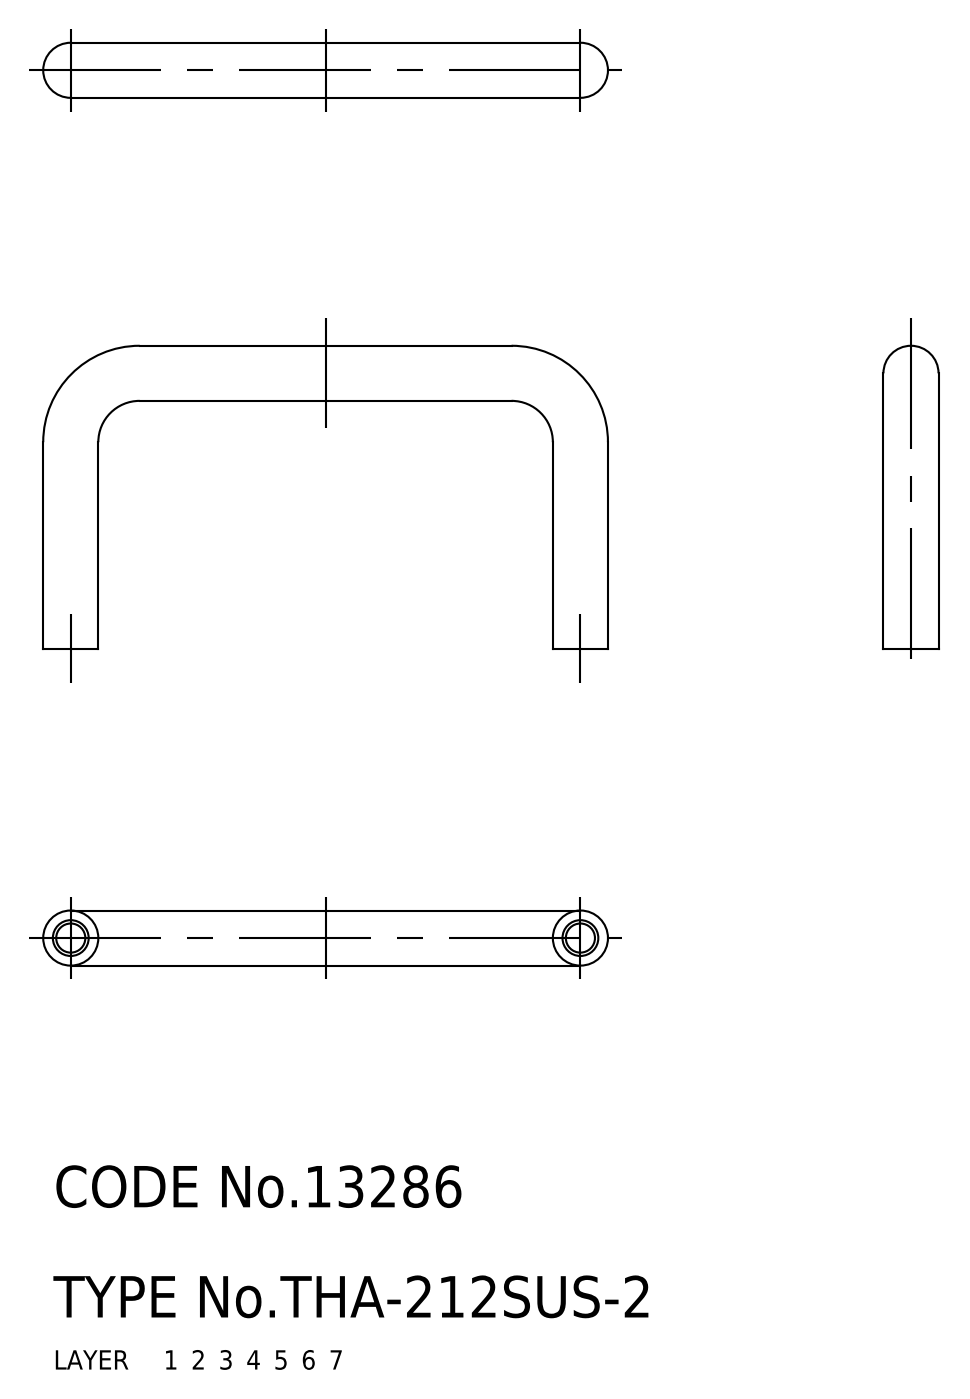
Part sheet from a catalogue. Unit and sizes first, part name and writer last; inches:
Units: inches
Overall size (bounding box): 1.614 × 0.866 × 0.157
Volume: 0.049 in³ · Surface area: 1.71 in²
Bodies: 1 solid, 18 faces (0 planar, 0 cylindrical, 18 other)
Part name (STEP PRODUCT): pull
STEP written by: CADfix (AUTOMOTIVE_DESIGN)
